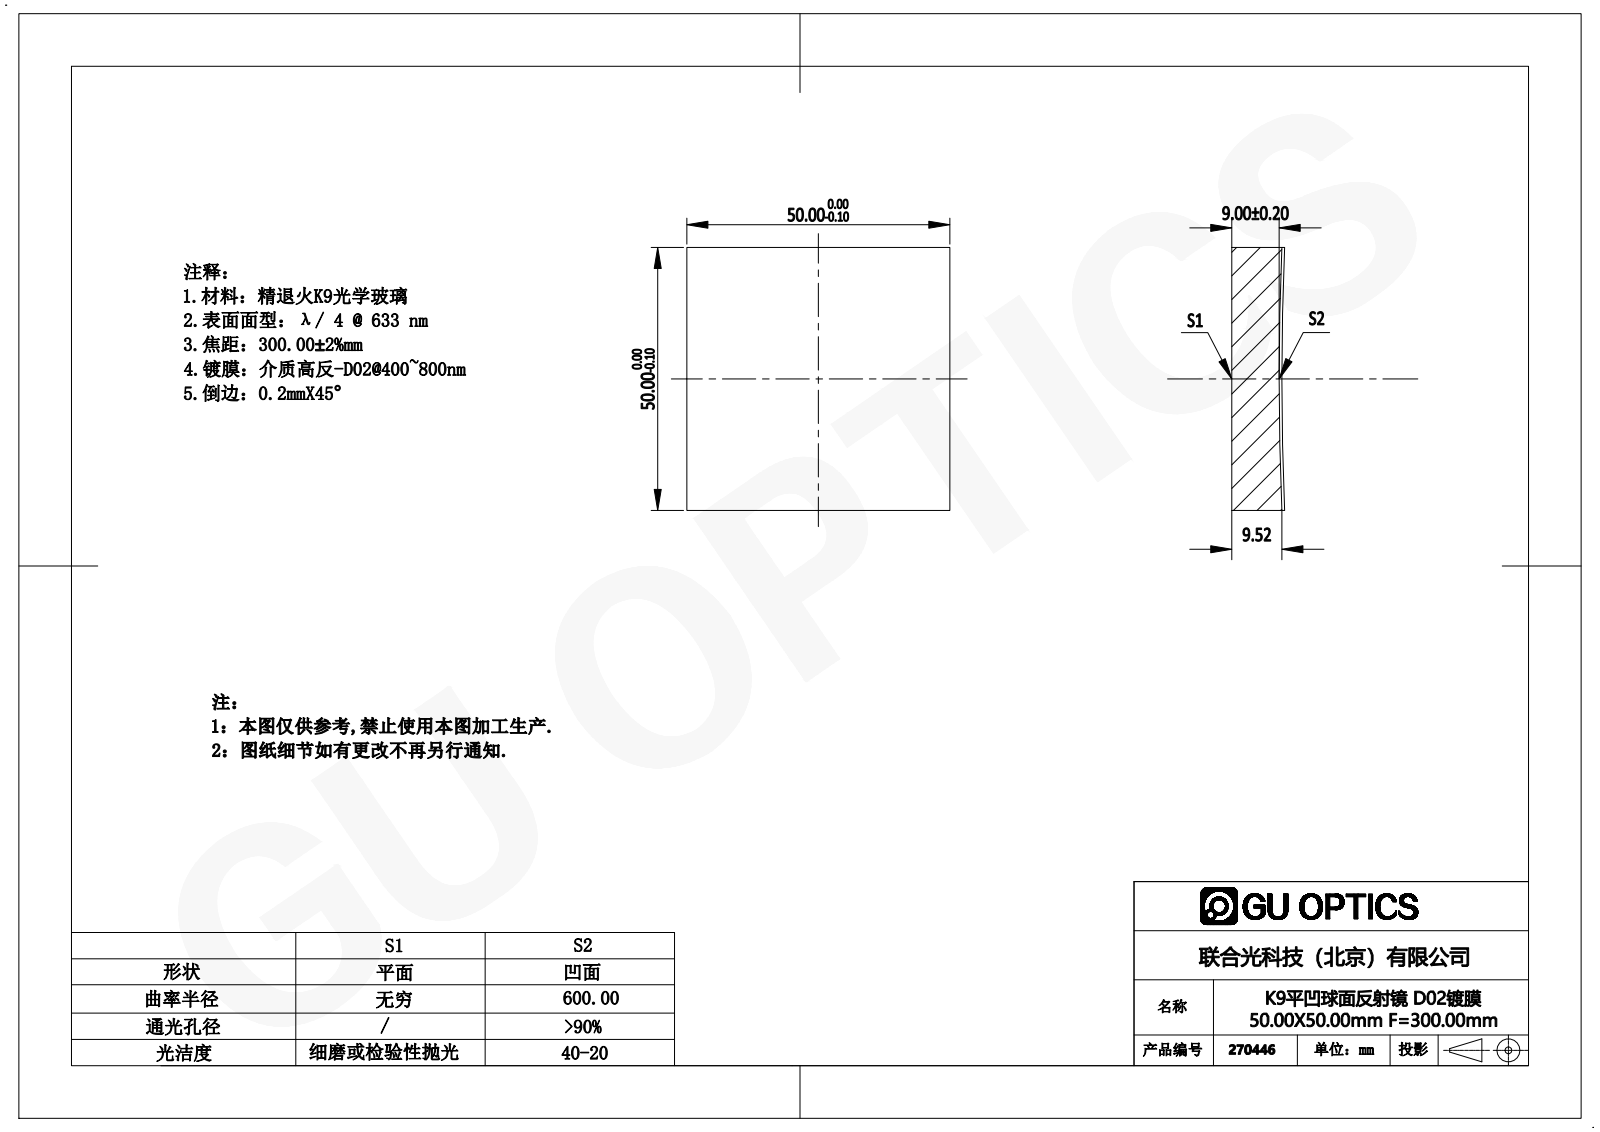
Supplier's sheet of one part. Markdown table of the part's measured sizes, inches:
| quantity | value |
| --- | --- |
| part name | 270056 |
| STEP written by | SolidWorks 2019 (AUTOMOTIVE_DESIGN) |
| units | inches |
| bodies | 1 solid, 7 faces (5 planar, 0 cylindrical, 2 other) |
| overall size | 1.969 × 1.969 × 0.395 |
| volume | 1.426 in³ |
| surface area | 10.76 in² |
| main face-to-face distances | 1.969 |
